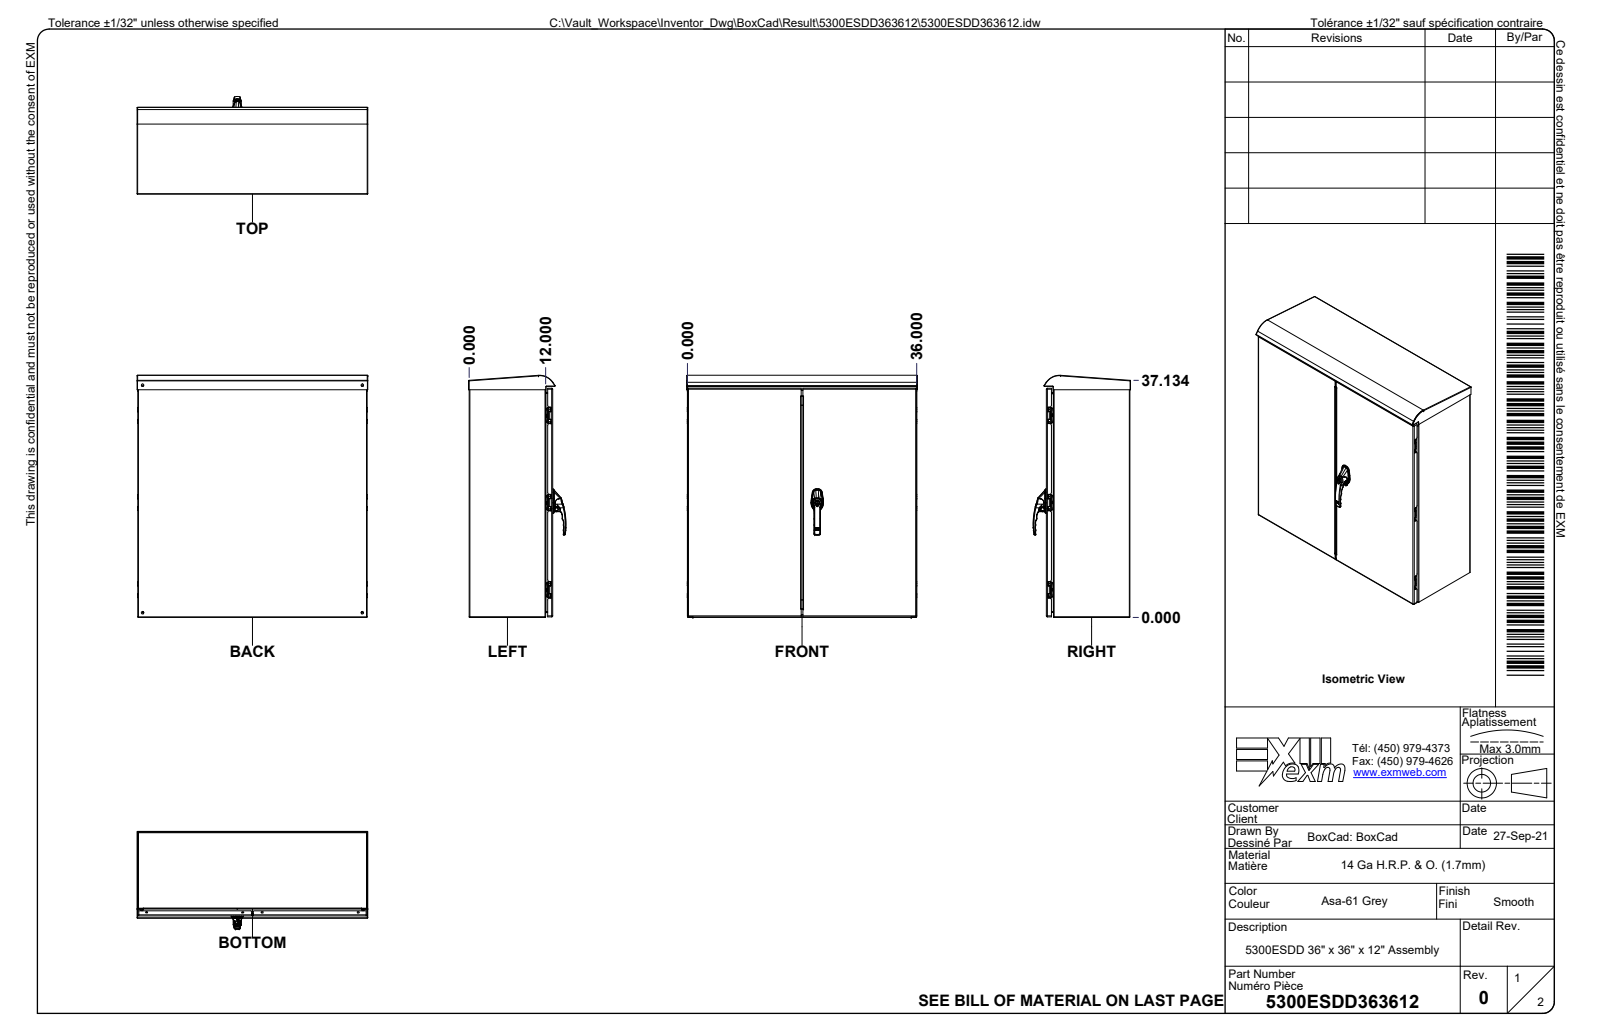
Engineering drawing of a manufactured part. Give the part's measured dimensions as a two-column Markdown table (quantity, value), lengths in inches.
| quantity | value |
| --- | --- |
| part name | 5300ESDD363612; 5300ESDD363612B; 5300ESDD363612B-P; 5300ESDD363612T-P (+8 more) |
| STEP written by | Autodesk Inventor 2024 (AUTOMOTIVE_DESIGN) |
| units | inches |
| bodies | 125 solids, 20375 faces (6247 planar, 4945 cylindrical, 9183 other) |
| overall size | 37.932 × 36.206 × 15.3 |
| volume | 498.7 in³ |
| surface area | 13 288 in² |
| round holes (diameter × count) | 0.043 × 18, 0.29 × 16, 0.03 × 14, 0.167 × 10, 0.315 × 10, 0.27 × 8, 0.178 × 6, 0.305 × 6, 0.5 × 6, 0.201 × 5, 0.39 × 4, 0.157 × 3 |
| round bosses / shafts (diameter × count) | 0.039 × 18, 0.03 × 13, 0.717 × 8, 0.311 × 8, 0.262 × 8, 0.232 × 7, 0.3 × 6, 0.199 × 6 |
| partial cylindrical surfaces (radius × count) | 0.02 × 365, 0.039 × 321, 0.01 × 307, 0.008 × 199, 0.004 × 102, 0.016 × 93, 0.079 × 83, 0.031 × 69 |
| main face-to-face distances | 0.068, 13.052, 12.983, 13.12, 0.105, 0.942, 0.874, 12.109, 12.178, 1.047 |
| hole center spacings | 16.125, 13.652, 36.056, 32.25, 0.394, 0.35, 0.735, 1.052 |
